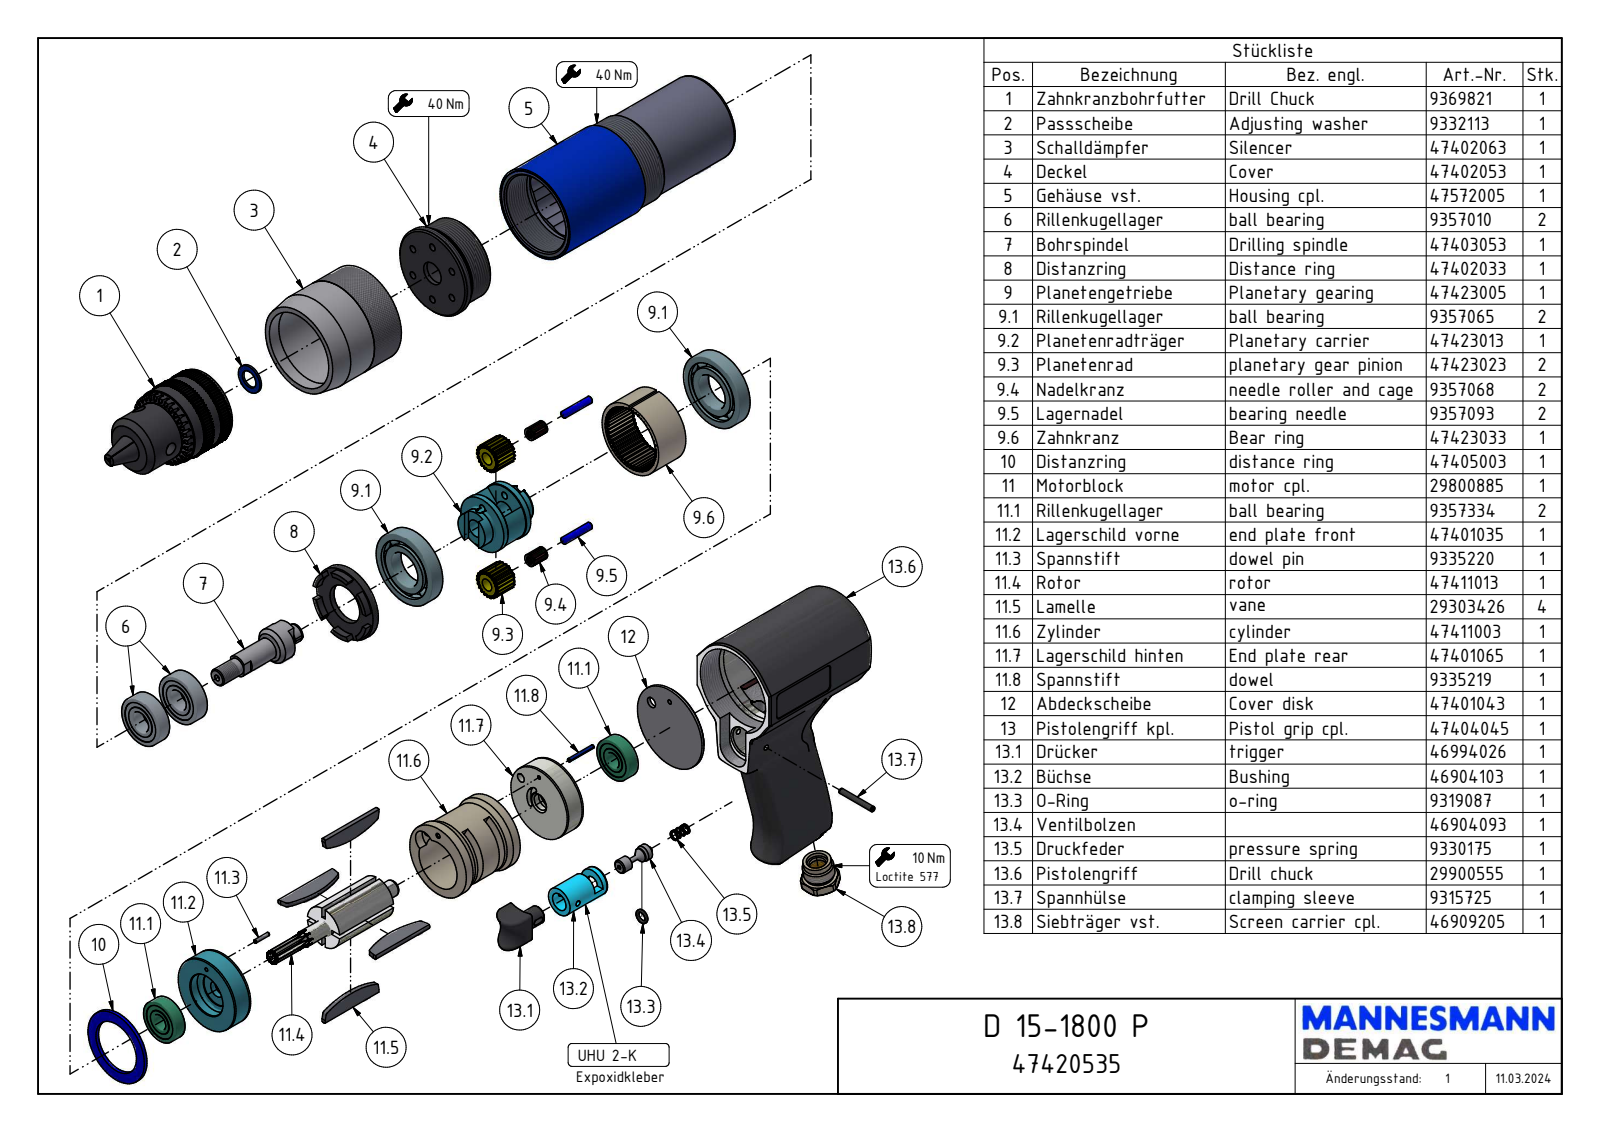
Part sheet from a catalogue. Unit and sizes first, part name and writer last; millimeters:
Units: millimetres
Overall size (bounding box): 227.3 × 147.91 × 54
Round holes (diameter × count): ⌀4 ×6, ⌀7 ×3, ⌀10 ×2, ⌀1.5 ×1, ⌀1.8 ×1, ⌀3 ×1, ⌀6 ×1, ⌀9 ×1, ⌀9.65 ×1, ⌀11.44 ×1, ⌀13 ×1, ⌀14 ×1
Round bosses / shafts (diameter × count): ⌀54 ×1, ⌀53.99 ×1, ⌀52 ×1, ⌀50 ×1, ⌀45.08 ×1, ⌀41.4 ×1, ⌀40 ×1, ⌀32 ×1
Partial cylindrical surfaces — rounded edges, fillets, slot ends (radius × count): R0.5 ×79, R2.5 ×6, R1.6 ×3, R2 ×3, R8 ×2, R7 ×1, R10 ×1, R10.5 ×1
Main face-to-face distances: 8.6, 71.3, 1, 7, 57, 0.5, 5, 102.2, 63.2, 6.2
Hole centre spacings: 16.75, 16.76, 29.02, 29.01, 33.5, 19.25, 31.2, 31.21
Volume: 512 642 mm³ · Surface area: 74 715 mm²
Bodies: 1 solid, 1429 faces (594 planar, 334 cylindrical, 501 other)
Part name (STEP PRODUCT): D 15-1800 P_47420535_1
STEP written by: Autodesk Inventor 2008 (AUTOMOTIVE_DESIGN)
